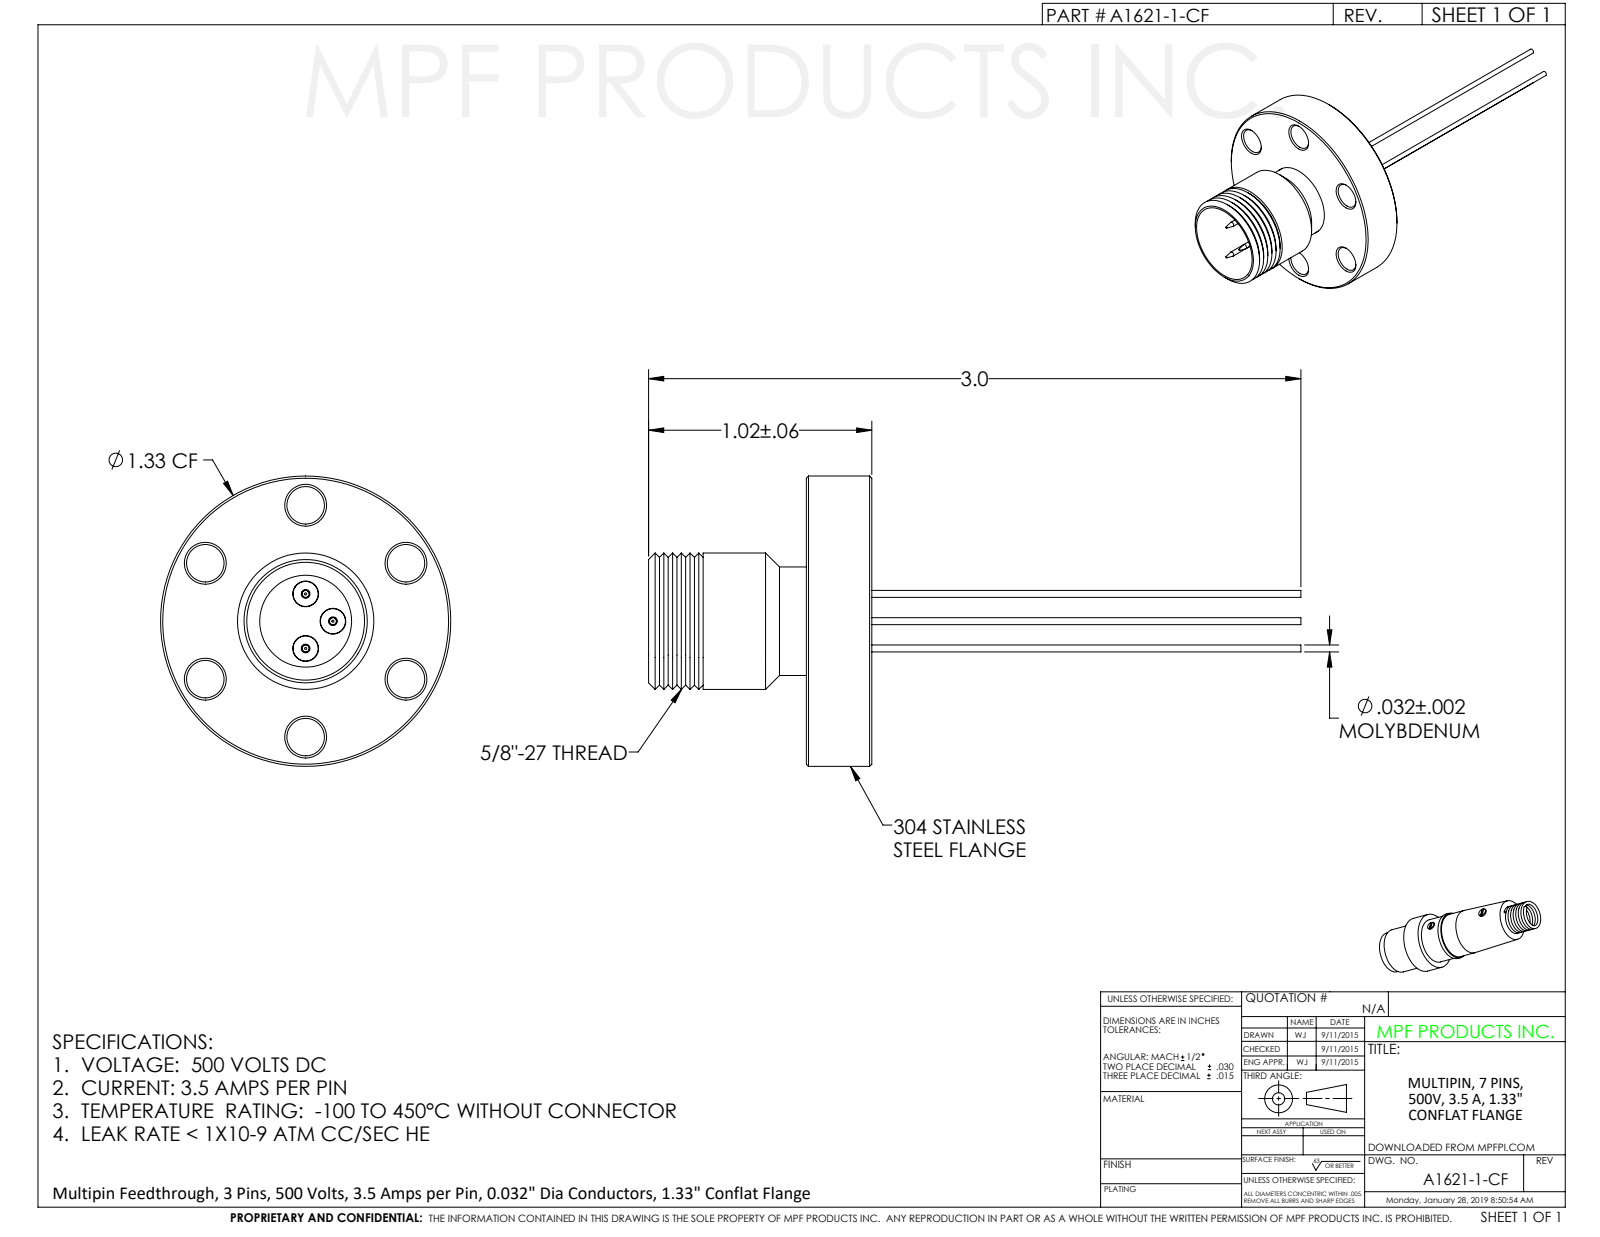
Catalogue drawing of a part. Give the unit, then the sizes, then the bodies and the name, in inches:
Units: inches
Overall size (bounding box): 2.99 × 1.33 × 1.33
Round holes (diameter × count): ⌀0.172 ×6, ⌀0.12 ×3, ⌀0.421 ×1, ⌀0.457 ×1, ⌀0.54 ×1, ⌀0.72 ×1, ⌀0.844 ×1
Round bosses / shafts (diameter × count): ⌀0.143 ×3, ⌀0.126 ×3, ⌀0.032 ×3, ⌀1.33 ×1, ⌀0.625 ×1, ⌀0.497 ×1
Main face-to-face distances: 0.285, 0.234, 0.051, 0.491, 0.206, 0.44, 0.266, 0.06, 0.5, 0.551
Hole centre spacings: 0.531, 0.92, 0.125, 0.177, 0.423, 0.432, 0.531, 0.539
Volume: 0.38 in³ · Surface area: 9.166 in²
Bodies: 1 solid, 146 faces (26 planar, 64 cylindrical, 56 other)
Part name (STEP PRODUCT): A1621-1-CF
STEP written by: SolidWorks 2012 (CONFIG_CONTROL_DESIGN)
